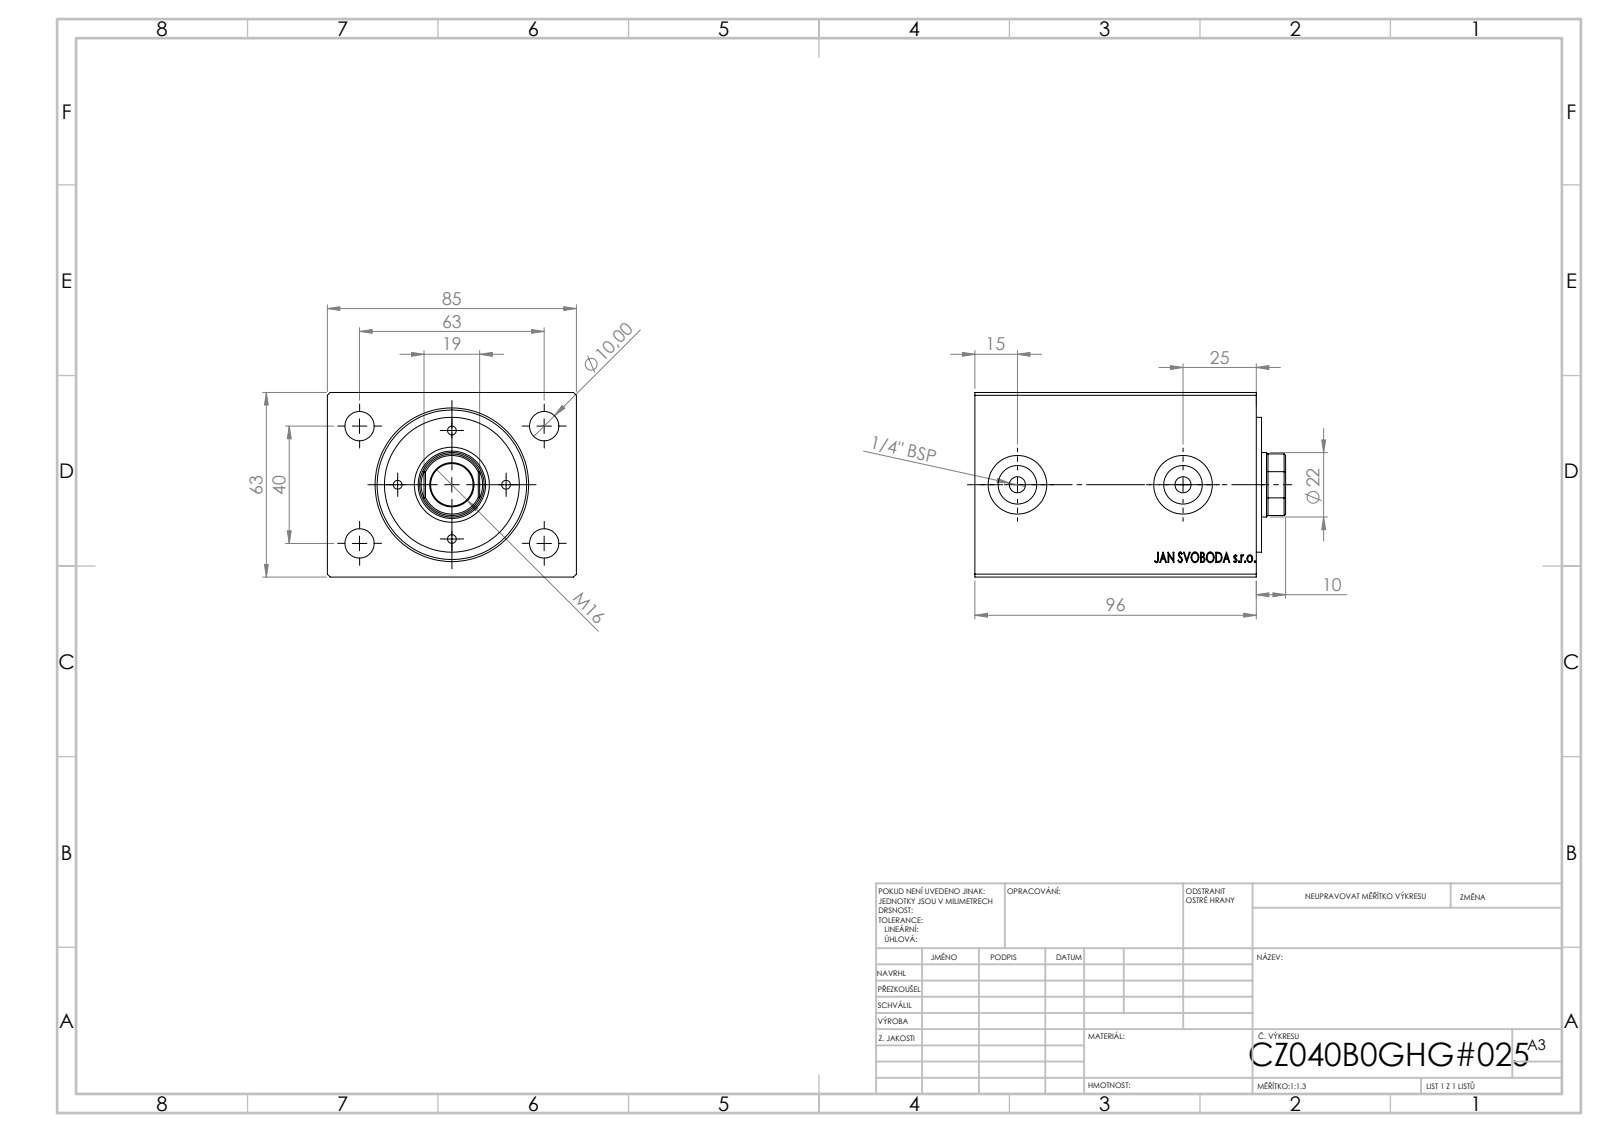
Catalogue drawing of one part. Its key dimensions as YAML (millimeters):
part_name: "V500CZ_B_VC; V500CZ"
step_written_by: "SolidWorks 2019 (CONFIG_CONTROL_DESIGN)"
units: millimeters
bodies: {solids: 3, faces: 873, planar: 399, cylindrical: 58, other: 416}
overall_size: [106, 85, 63]
volume: 511454
surface_area: 90624
round_holes:
  - {diameter: 3, count: 4}
  - {diameter: 10, count: 4}
  - {diameter: 5.5, count: 2}
  - {diameter: 13.16, count: 2}
  - {diameter: 20, count: 2}
  - {diameter: 14.5, count: 1}
  - {diameter: 22, count: 1}
  - {diameter: 23, count: 1}
  - {diameter: 36, count: 1}
  - {diameter: 40, count: 1}
  - {diameter: 51, count: 1}
round_bosses_or_shafts:
  - {diameter: 46, count: 1}
partial_cylinders:
  - {radius: 10.5, count: 1}
face_to_face_distances: [63, 85, 96, 81.3, 14.7, 71, 10.3, 25, 1.8, 72.8]
hole_center_spacings: [18.5, 23.85, 26.16, 31.54, 37.31, 49.74, 53.85, 37]
